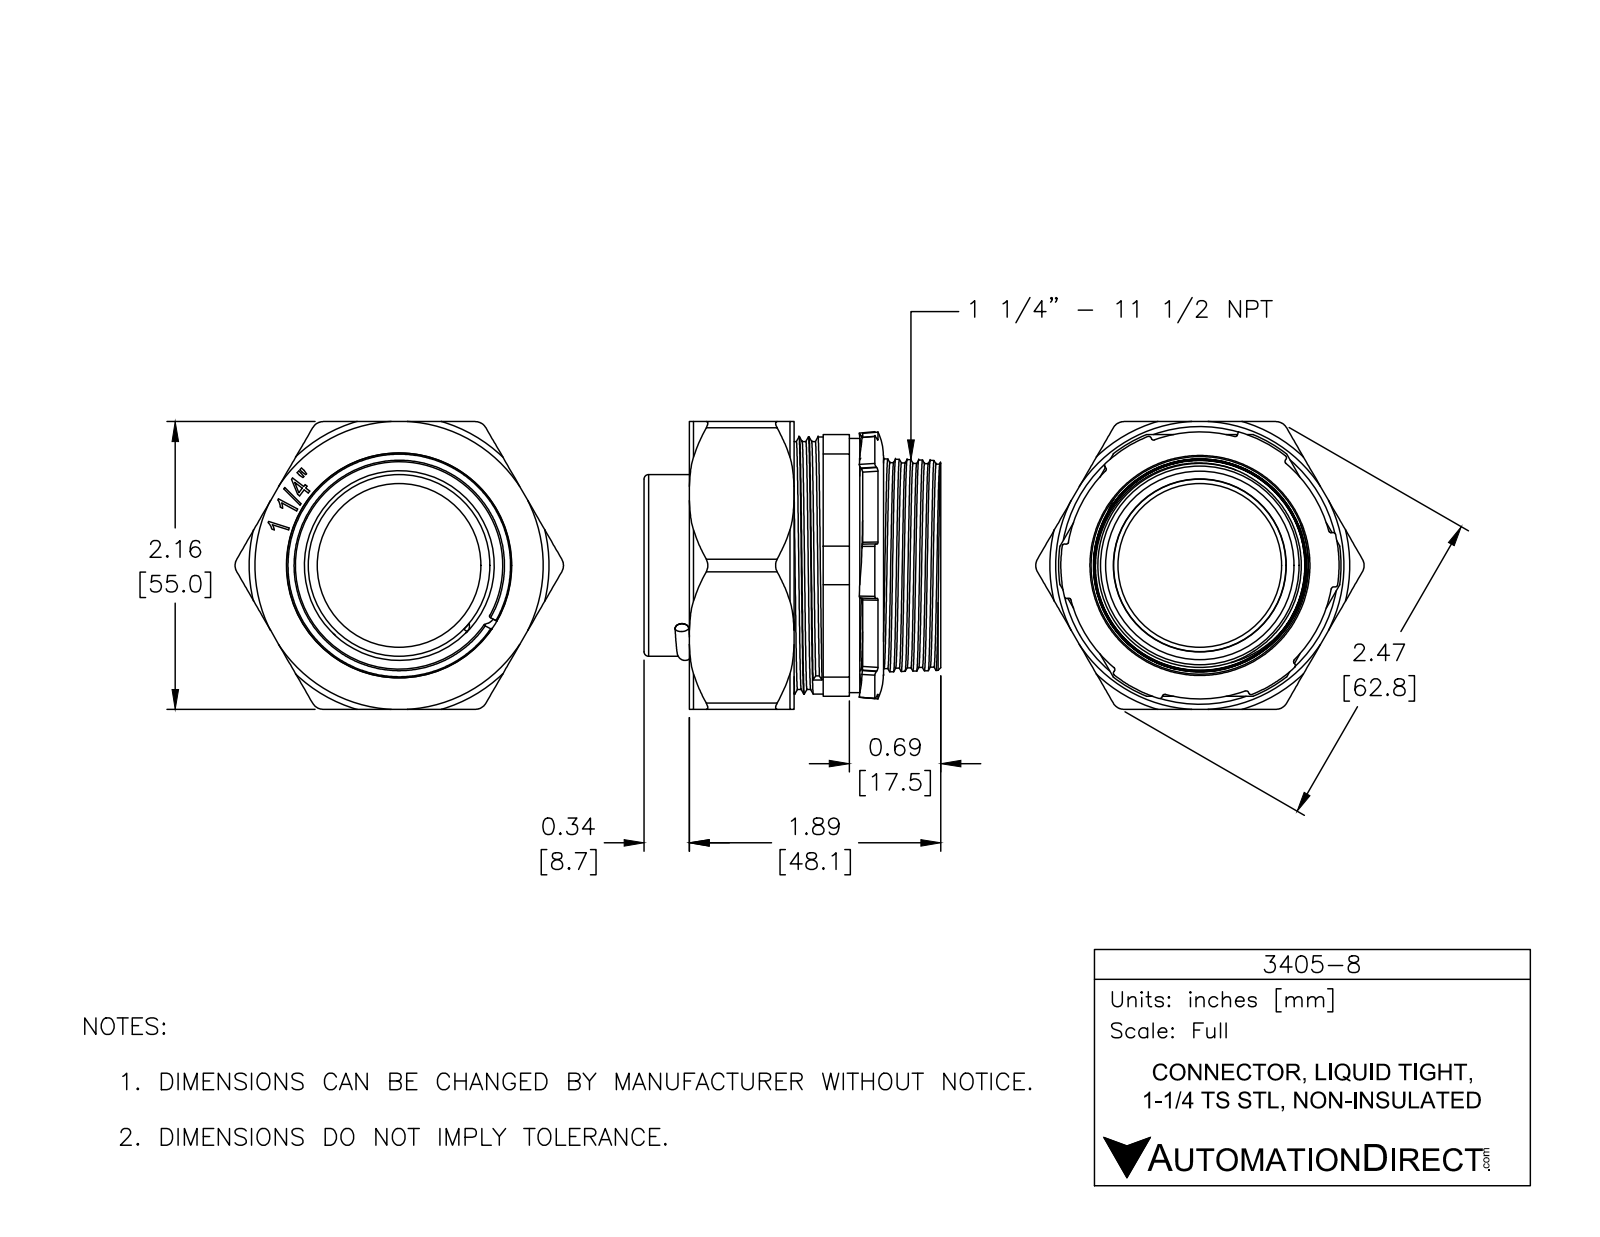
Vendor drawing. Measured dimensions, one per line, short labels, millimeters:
name: 3405-8
written by: SolidWorks 2018 (AUTOMOTIVE_DESIGN)
unit: mm
bodies: 6 solids, 524 faces (212 planar, 122 cylindrical, 190 other)
size: 62.8 × 56.7 × 55
volume: 39 180 mm³; area: 41 320 mm²
holes: 1× ⌀4.6, 1× ⌀31.3, 1× ⌀33, 1× ⌀36, 1× ⌀39.5, 1× ⌀41.6, 1× ⌀42.3, 1× ⌀43, 1× ⌀44.7, 1× ⌀48.5
bosses: 1× ⌀49.1, 1× ⌀48.6, 1× ⌀47.5, 1× ⌀47.4, 1× ⌀44, 1× ⌀34.7, 1× ⌀33, 1× ⌀3.8
rounds: 8× R0.3, 6× R2.4, 2× R0.1, 2× R1.3, 1× R0.2, 1× R0.4, 1× R0.6, 1× R27
face distances: 55, 30.6, 2.5, 52.5, 32.6, 2, 23.6, 7, 9, 10.6
hole spacings: 24.5
